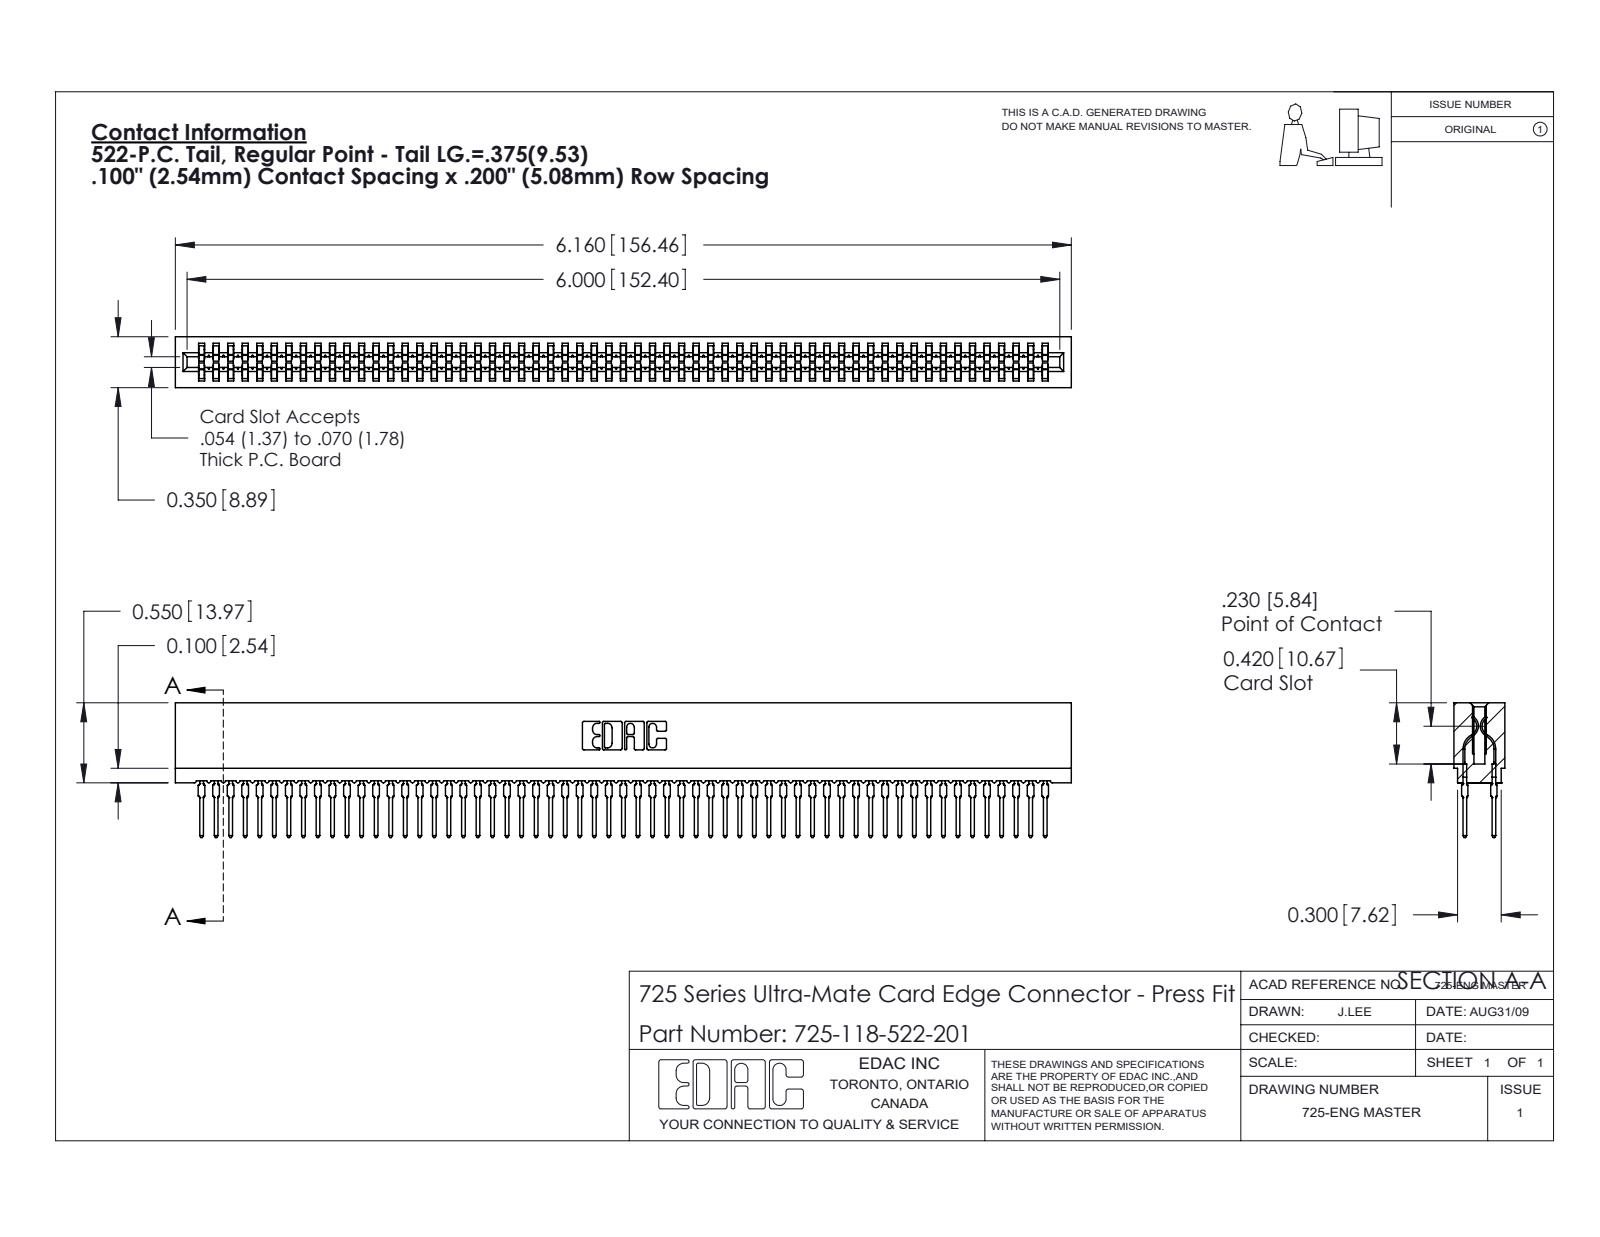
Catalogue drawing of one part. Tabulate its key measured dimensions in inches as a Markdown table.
| quantity | value |
| --- | --- |
| part name | 725-118-522-201; 745-292-001_522; 725 Part_Insulator Option - 01 |
| STEP written by | SolidWorks 2020 (CONFIG_CONTROL_DESIGN) |
| units | inches |
| bodies | 119 solids, 10656 faces (5483 planar, 2105 cylindrical, 3068 other) |
| overall size | 6.16 × 0.926 × 0.35 |
| volume | 0.76 in³ |
| surface area | 41.99 in² |
| partial cylindrical surfaces (radius × count) | 0.021 × 236, 0.015 × 118, 0.01 × 22, 0.005 × 8, 0.011 × 8, 0.007 × 6, 0.031 × 6, 0.026 × 3 |
| main face-to-face distances | 0.063, 0.287, 0.35, 0.2, 0.212, 0.138, 0.076, 0.149, 0.045, 0.305 |
